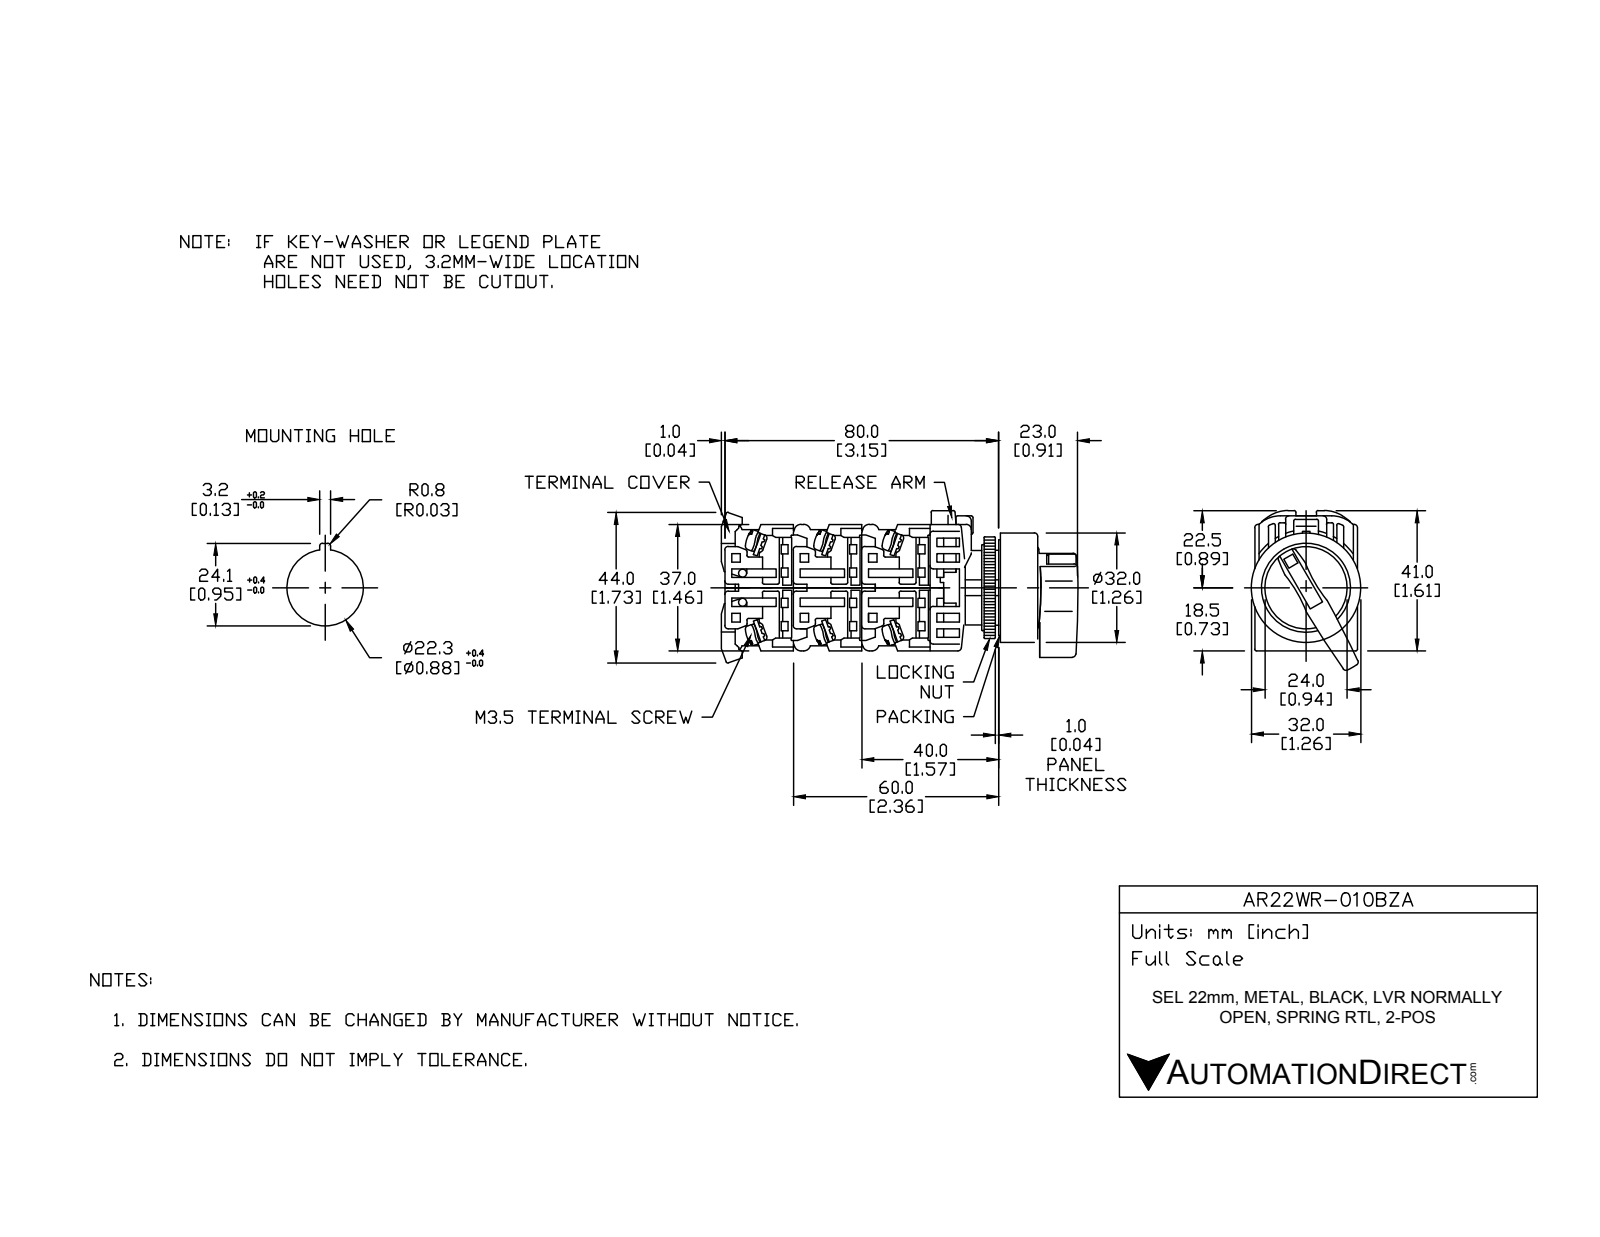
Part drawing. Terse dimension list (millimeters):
name: AR22WR-010BZA
written by: SolidWorks 2017 (AUTOMOTIVE_DESIGN)
unit: mm
bodies: 12 solids, 327 faces (222 planar, 84 cylindrical, 21 other)
size: 64 × 43.49 × 36.49
volume: 30 260 mm³; area: 20 554 mm²
holes: 1× ⌀21.8, 1× ⌀22, 1× ⌀25, 1× ⌀31
bosses: 2× ⌀5, 1× ⌀32, 1× ⌀30.5, 1× ⌀29.8, 1× ⌀24, 1× ⌀21.75, 1× ⌀17
rounds: 23× R0.5, 10× R1, 4× R1.75, 4× R5, 2× R4, 1× R16.59, 1× R17.59
face distances: 1, 3, 28.5, 18, 11, 2, 29, 30, 10.5, 0.5
